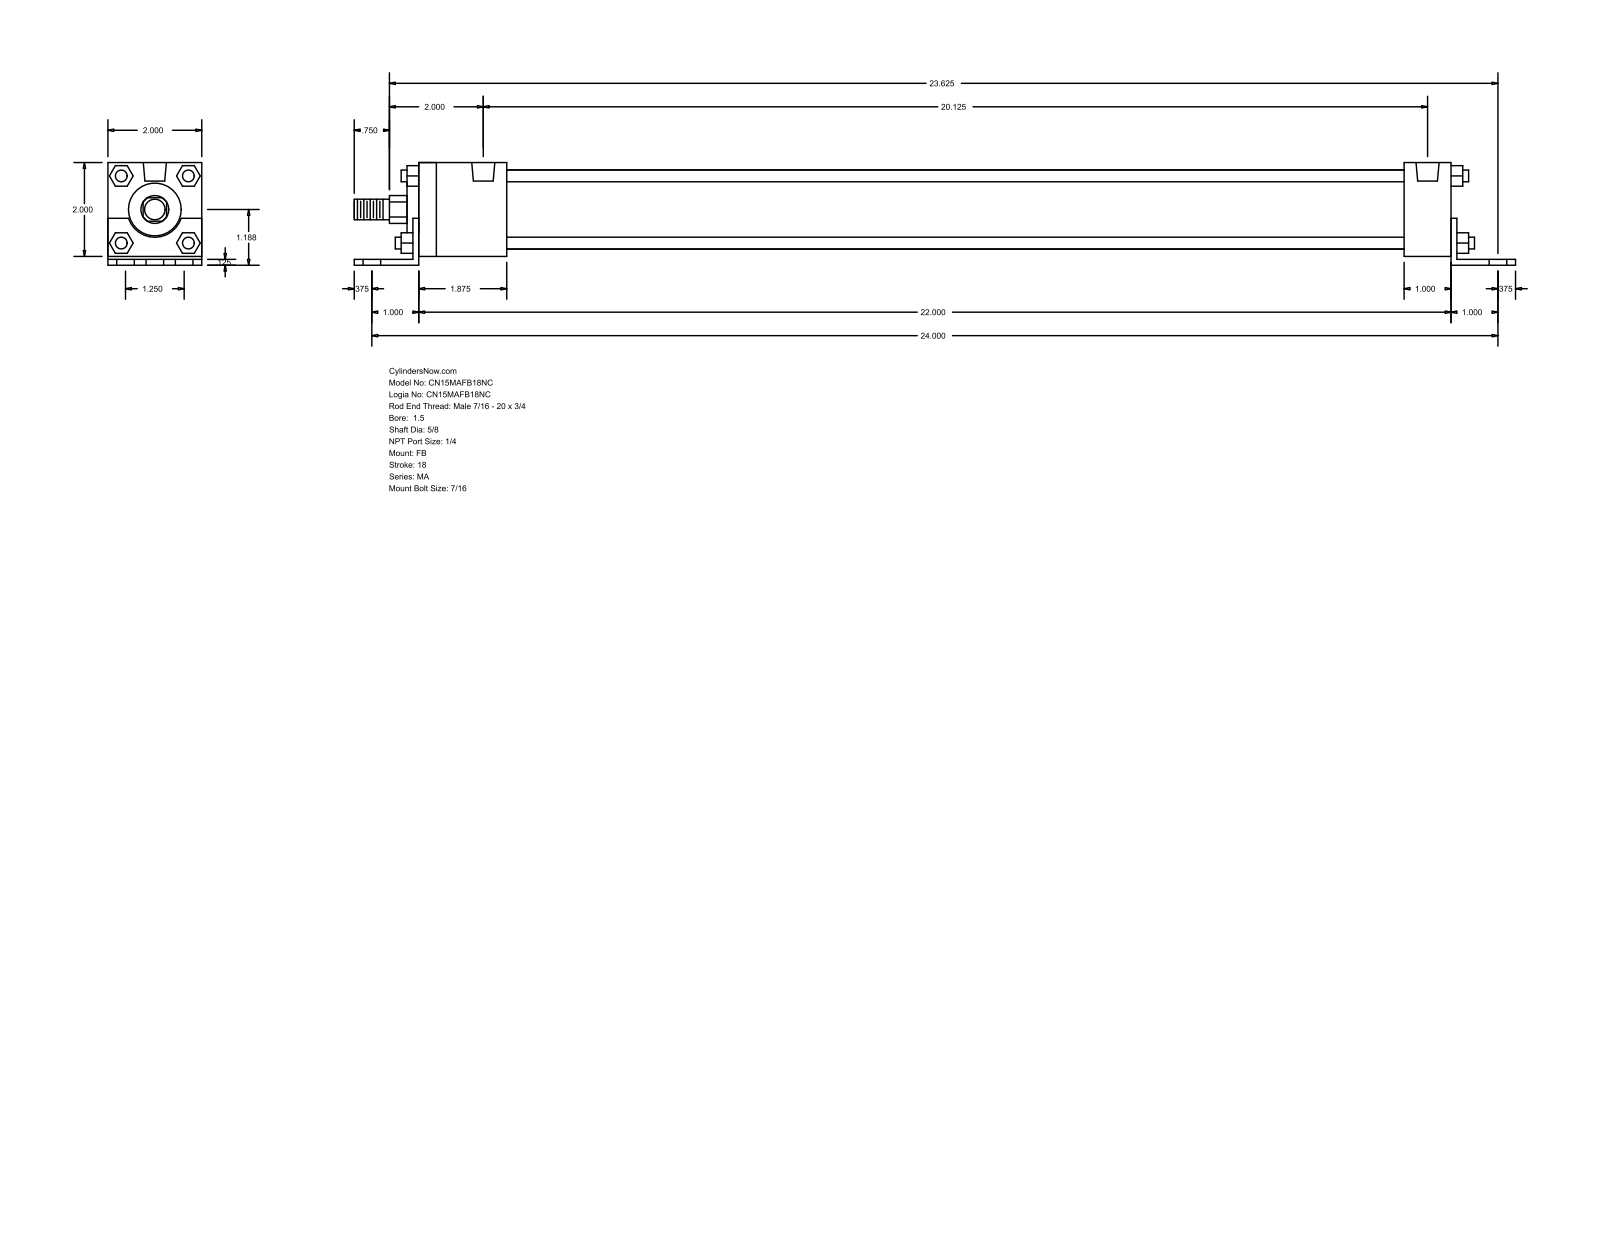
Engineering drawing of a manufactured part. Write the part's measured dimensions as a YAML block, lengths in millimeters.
part_name: "MA_FB__0150_0.625"
step_written_by: "GSSL Pune (CONFIG_CONTROL_DESIGN)"
units: millimeters
bodies: {solids: 0, faces: 140, planar: 105, cylindrical: 35, other: 0}
overall_size: [628.65, 55.56, 50.8]
round_holes:
  - {diameter: 11.11, count: 6}
  - {diameter: 7.94, count: 4}
  - {diameter: 12.49, count: 2}
round_bosses_or_shafts:
  - {diameter: 6.35, count: 4}
  - {diameter: 42.93, count: 1}
  - {diameter: 28.57, count: 1}
  - {diameter: 15.88, count: 1}
  - {diameter: 11.11, count: 1}
partial_cylinders:
  - {radius: 7.54, count: 1}
  - {radius: 15.05, count: 1}
face_to_face_distances: [50.8, 3.17, 4.76, 55.56, 1.59, 52.39, 3.18, 25.4, 561.97, 568.32]
hole_center_spacings: [15.88, 609.82, 609.61, 31.76, 41.28, 62.38, 511.18, 549.51]
